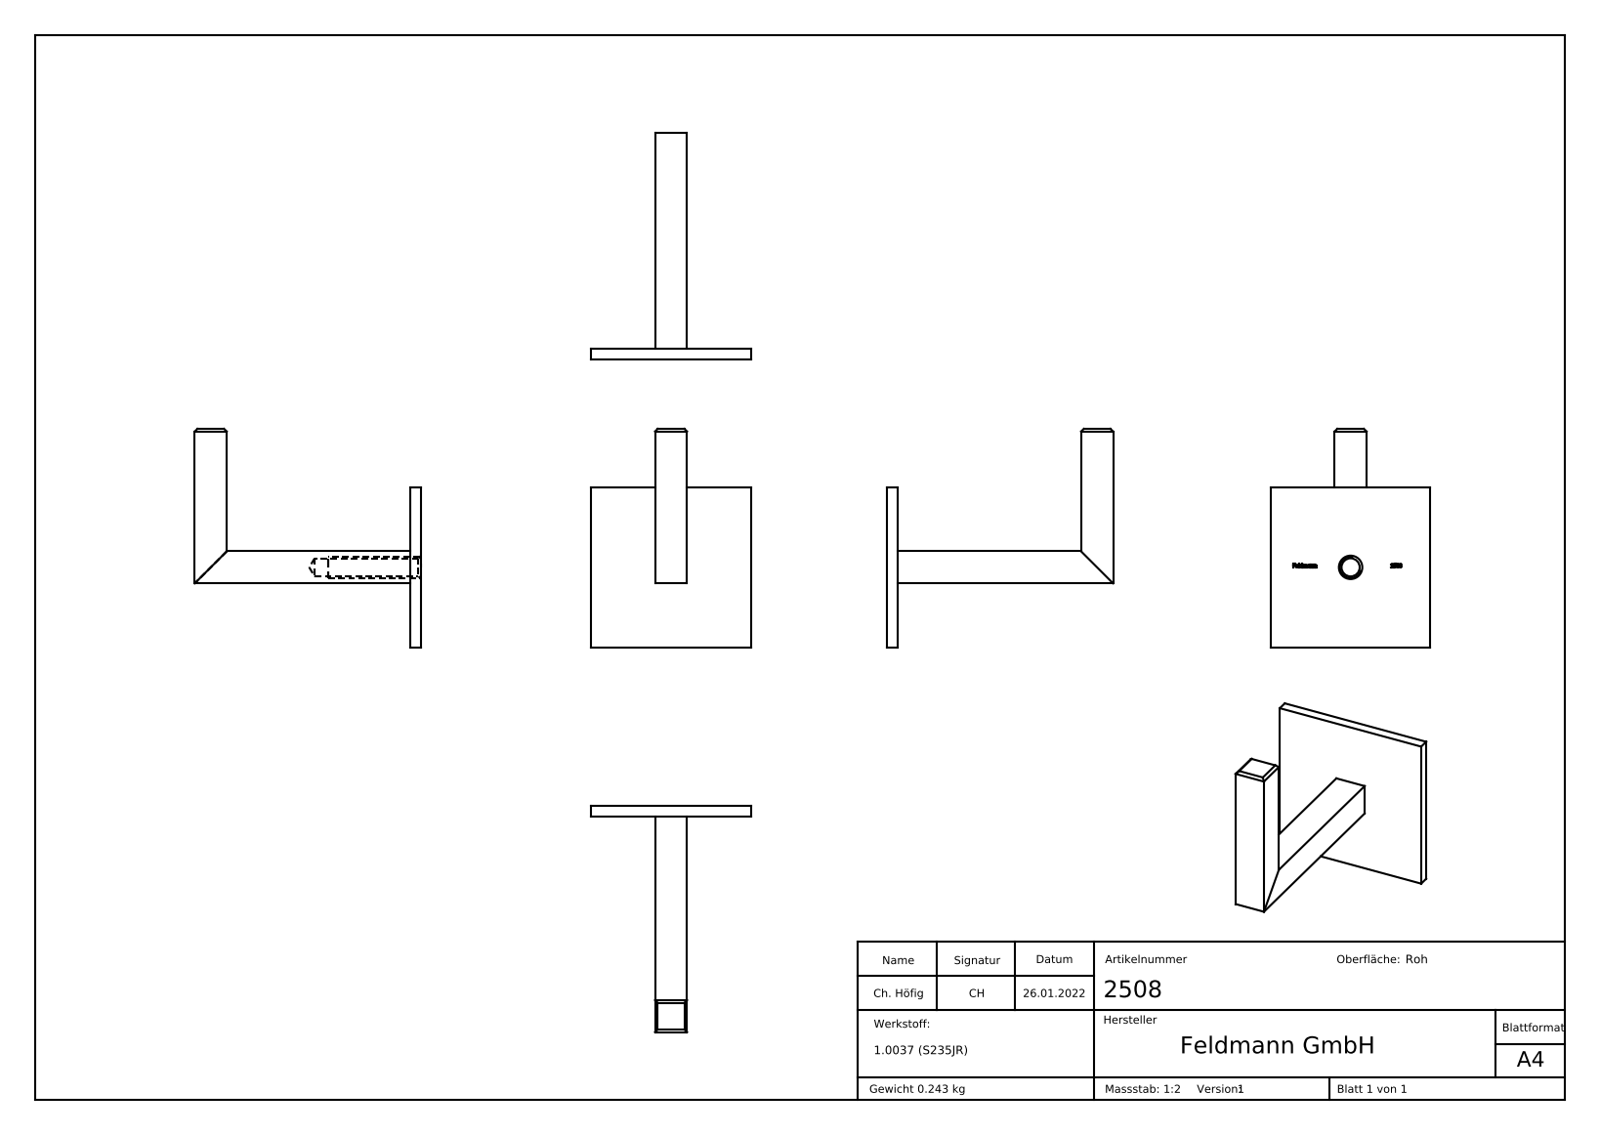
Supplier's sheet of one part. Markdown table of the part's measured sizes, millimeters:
| quantity | value |
| --- | --- |
| part name | 2508 |
| STEP written by | SolidWorks 2018 (CONFIG_CONTROL_DESIGN) |
| units | millimeters |
| bodies | 1 solid, 132 faces (20 planar, 83 cylindrical, 29 other) |
| overall size | 85 × 82 × 60 |
| volume | 30 913 mm³ |
| surface area | 15 578 mm² |
| round holes (diameter × count) | 6.8 × 1 |
| partial cylindrical surfaces (radius × count) | 0.1 × 20, 0.5 × 6 |
| main face-to-face distances | 4, 12, 24, 36, 85, 81, 73, 69, 60, 82 |
